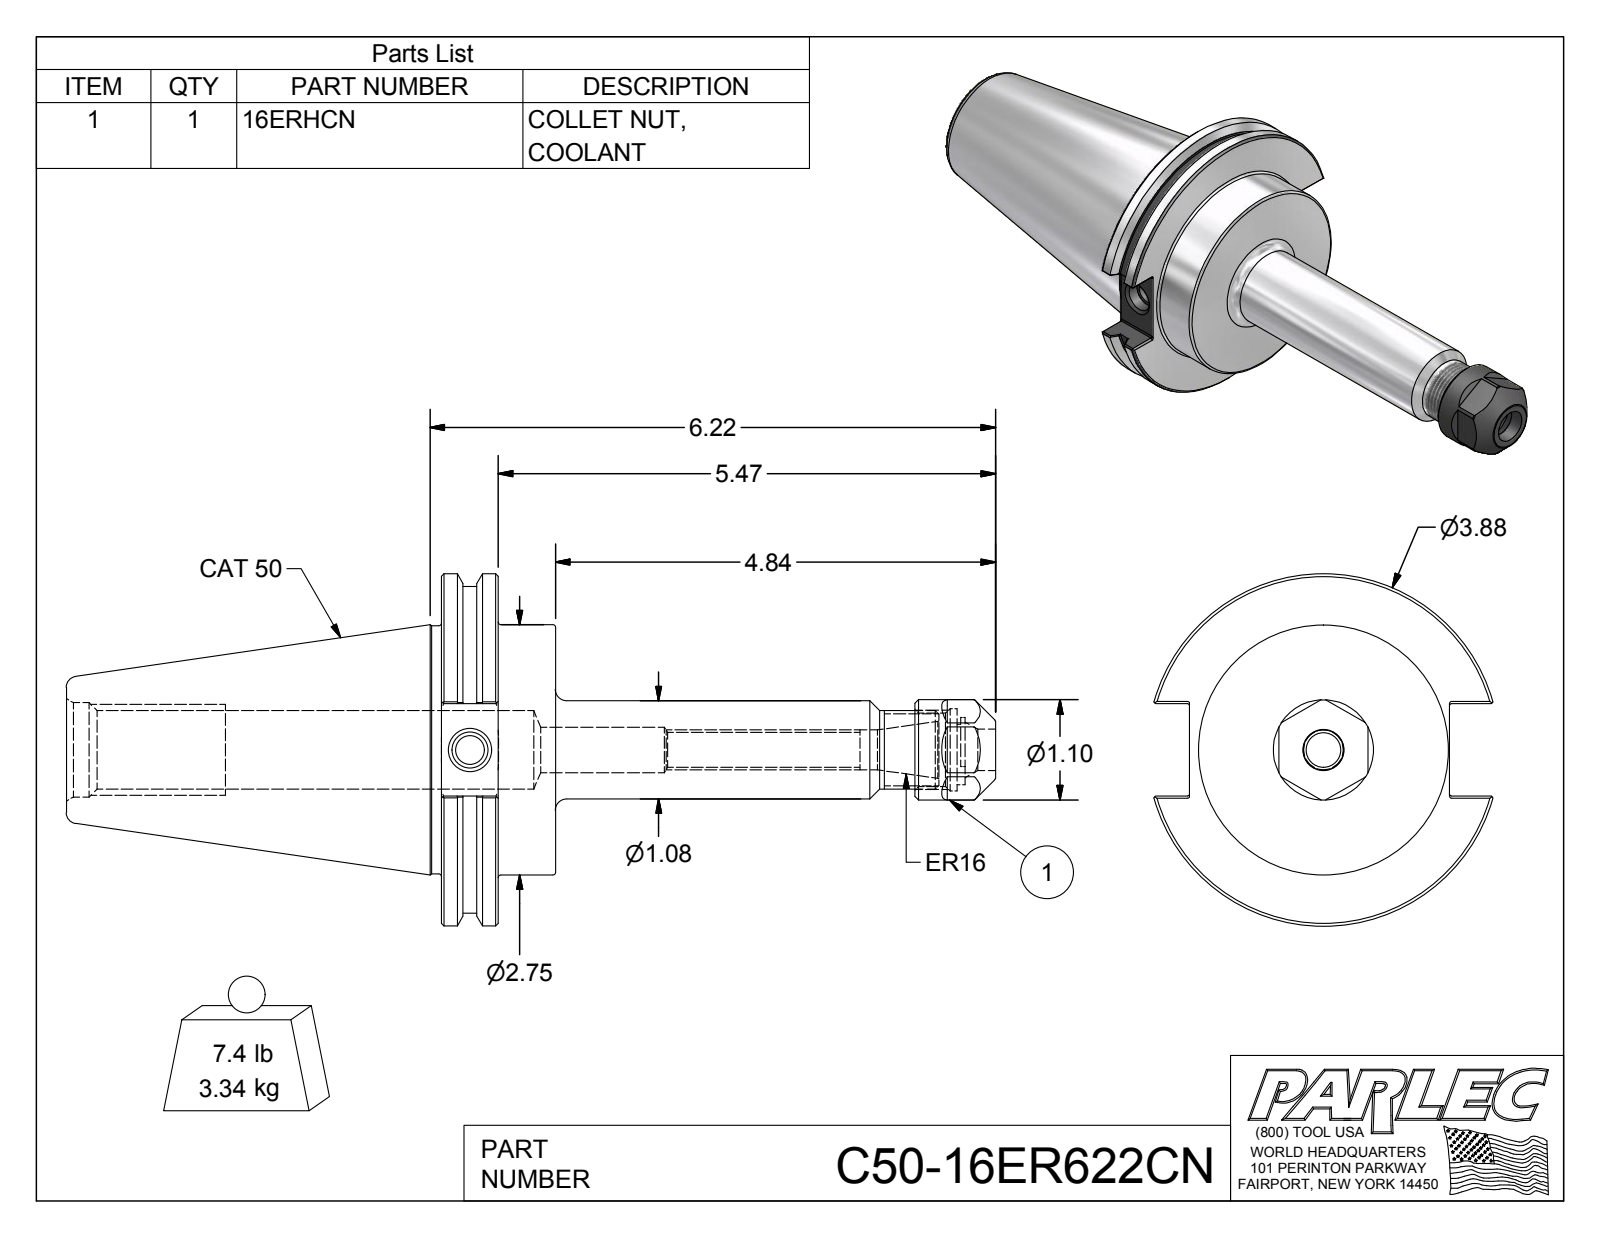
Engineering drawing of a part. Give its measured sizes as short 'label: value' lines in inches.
name: C50-16ER622CN; C50-16ER6-1; 16ERHCN
written by: Autodesk Inventor 2012 (AUTOMOTIVE_DESIGN)
unit: in
bodies: 2 solids, 130 faces (50 planar, 35 cylindrical, 45 other)
size: 10.22 × 3.875 × 3.729
volume: 26.17 in³; area: 100.7 in²
holes: 1× ⌀0.315, 1× ⌀0.383, 1× ⌀0.399, 1× ⌀0.44, 1× ⌀0.453, 1× ⌀0.5, 1× ⌀0.661, 1× ⌀0.807, 1× ⌀0.865, 1× ⌀0.906, 1× ⌀1.038
bosses: 1× ⌀3.875, 1× ⌀3.594, 1× ⌀2.75, 1× ⌀2.73, 1× ⌀1.102, 1× ⌀1.08, 1× ⌀0.866
rounds: 12× R0.02, 1× R0.354
face distances: 1.255, 0.625, 0.63, 0.979, 4.125, 4.75, 5.38, 2.86, 1.015, 0.866
hole spacings: 0.051
